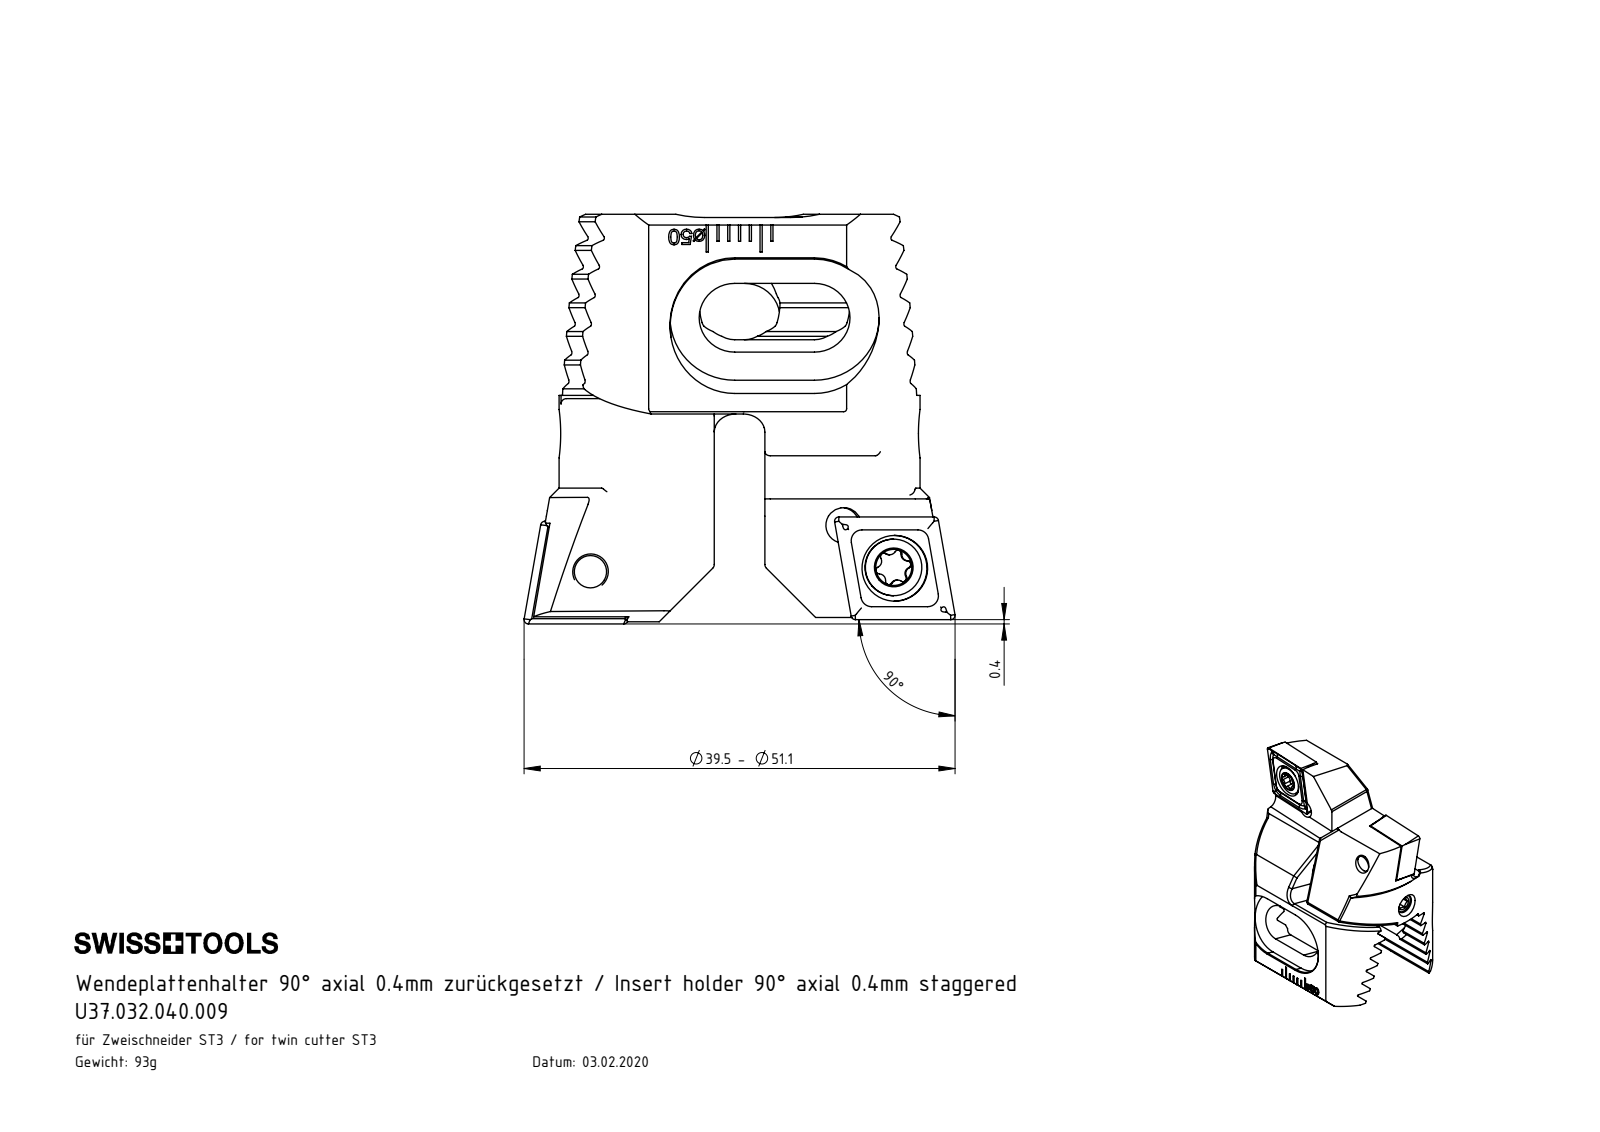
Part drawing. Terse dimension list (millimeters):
name: ZC3-xxx.001.021_A; WCB-ER2.001.009_A; Z32-ER3.001.013_A; CCMT09T304 (+2 more)
written by: SolidWorks 2017 (AUTOMOTIVE_DESIGN)
unit: mm
bodies: 8 solids, 580 faces (298 planar, 104 cylindrical, 178 other)
size: 40 × 38 × 26.2
volume: 11 842 mm³; area: 8 242 mm²
holes: 4× ⌀1.6, 4× ⌀3.3, 2× ⌀4.4, 2× ⌀6.1, 1× ⌀2, 1× ⌀3.5
bosses: 3× ⌀4, 2× ⌀5.25
rounds: 16× R0.5, 12× R0.2, 12× R0.34, 12× R0.59, 4× R2, 4× R3.3, 4× R6, 4× R12
face distances: 2.38, 4.76, 9.53, 7.15, 4.89, 11.91, 7.14, 1.27, 4.77, 2.39
hole spacings: 6.07, 6.19, 9, 28.65, 2.49, 2.51, 5, 9.34
